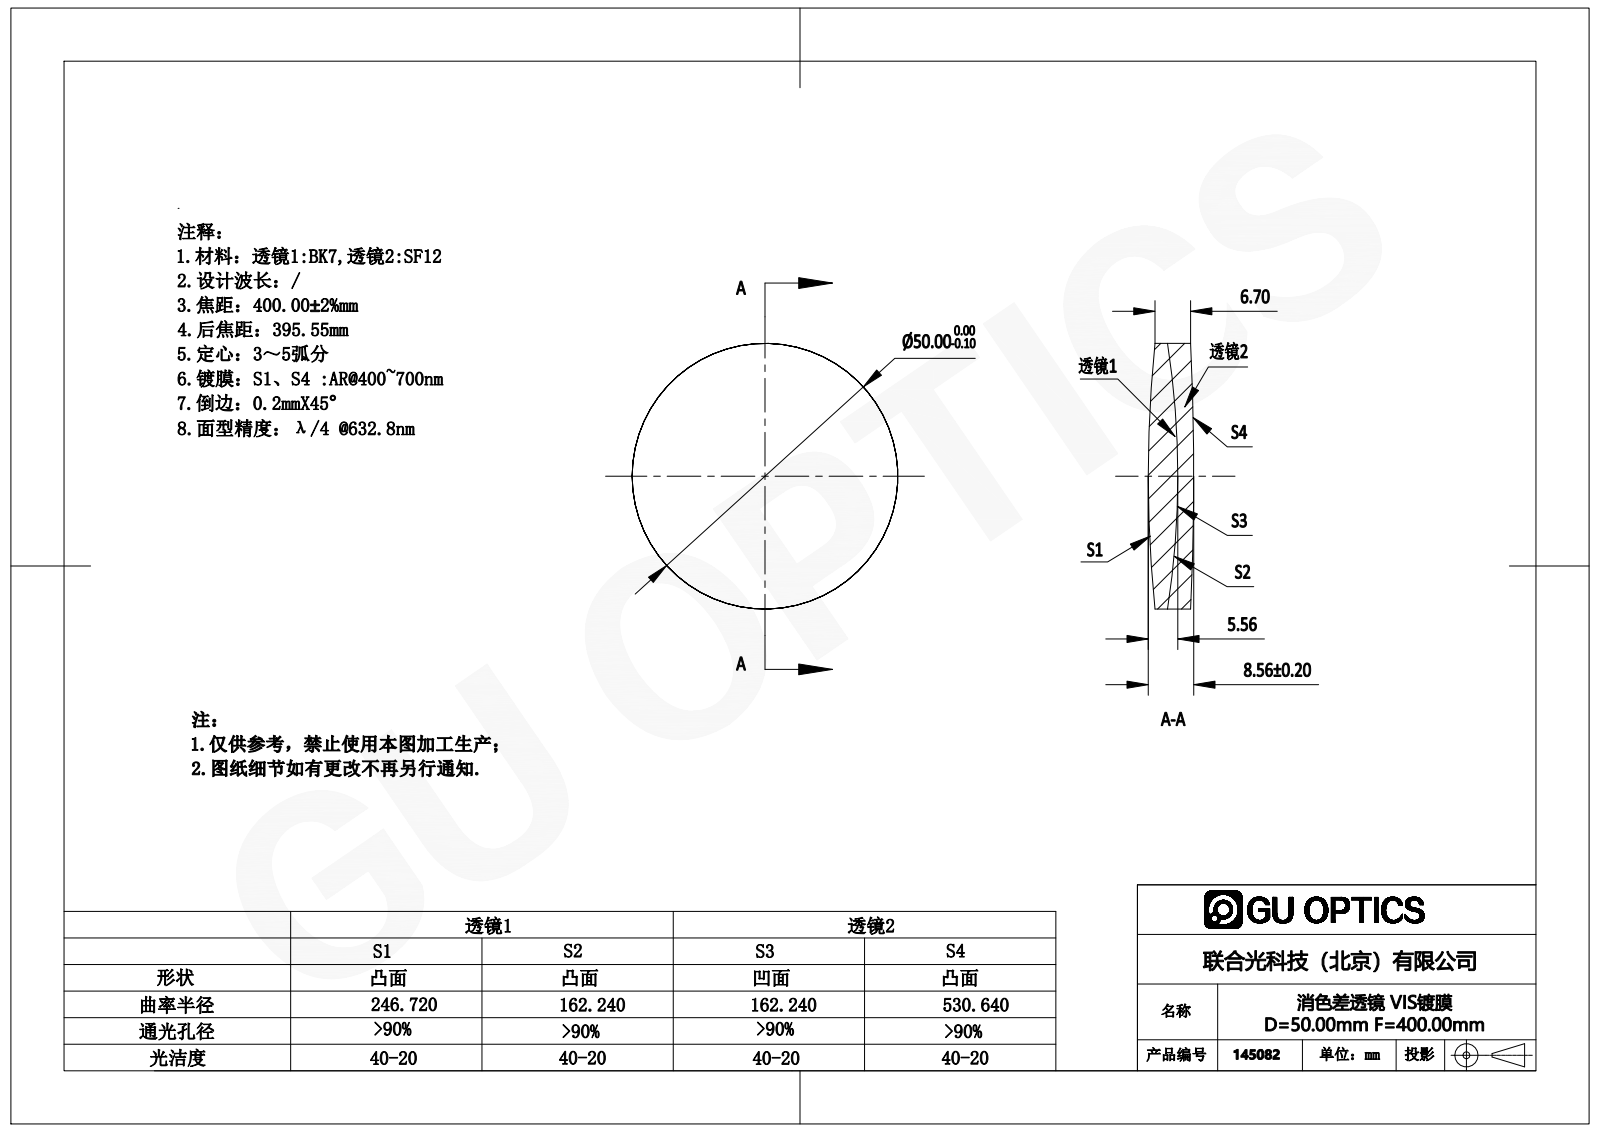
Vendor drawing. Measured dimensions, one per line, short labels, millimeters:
name: 145082
written by: SolidWorks 2016 (AUTOMOTIVE_DESIGN)
unit: mm
bodies: 2 solids, 12 faces (0 planar, 4 cylindrical, 8 other)
size: 50 × 50 × 8.56
volume: 14 984 mm³; area: 8 936 mm²
bosses: 1× ⌀50
